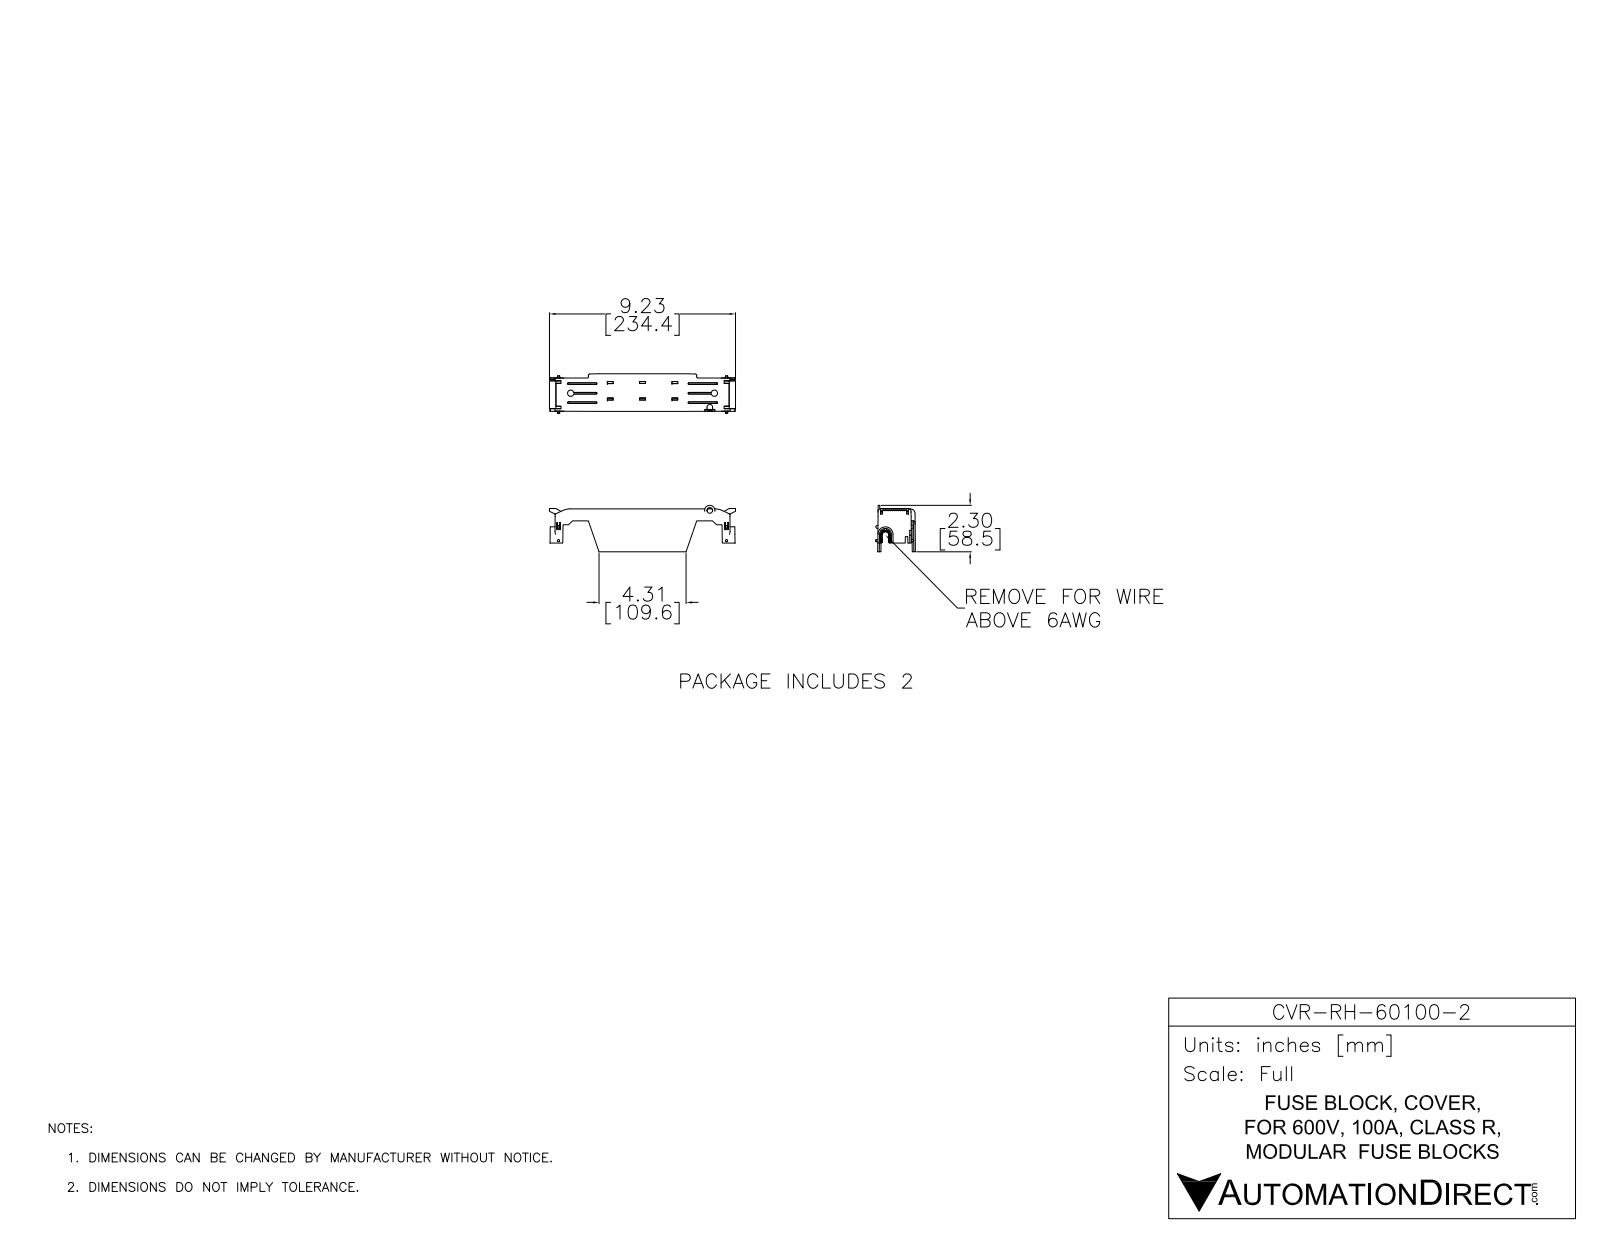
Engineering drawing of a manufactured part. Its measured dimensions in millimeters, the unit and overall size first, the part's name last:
Units: millimetres
Overall size (bounding box): 234.4 × 58.5 × 49.9
Round holes (diameter × count): ⌀7 ×1
Partial cylindrical surfaces — rounded edges, fillets, slot ends (radius × count): R1 ×18, R3 ×14, R0.8 ×6, R1.5 ×4, R0.3 ×2, R0.5 ×2, R4.2 ×2, R16 ×2
Main face-to-face distances: 2, 5, 3, 7, 4, 20.4, 25.1, 27.1, 30.1, 32.1
Volume: 67 020 mm³ · Surface area: 71 030 mm²
Bodies: 1 solid, 1436 faces (948 planar, 102 cylindrical, 386 other)
Part name (STEP PRODUCT): CVR-RH-60100-2
STEP written by: SolidWorks 2017 (AUTOMOTIVE_DESIGN)
